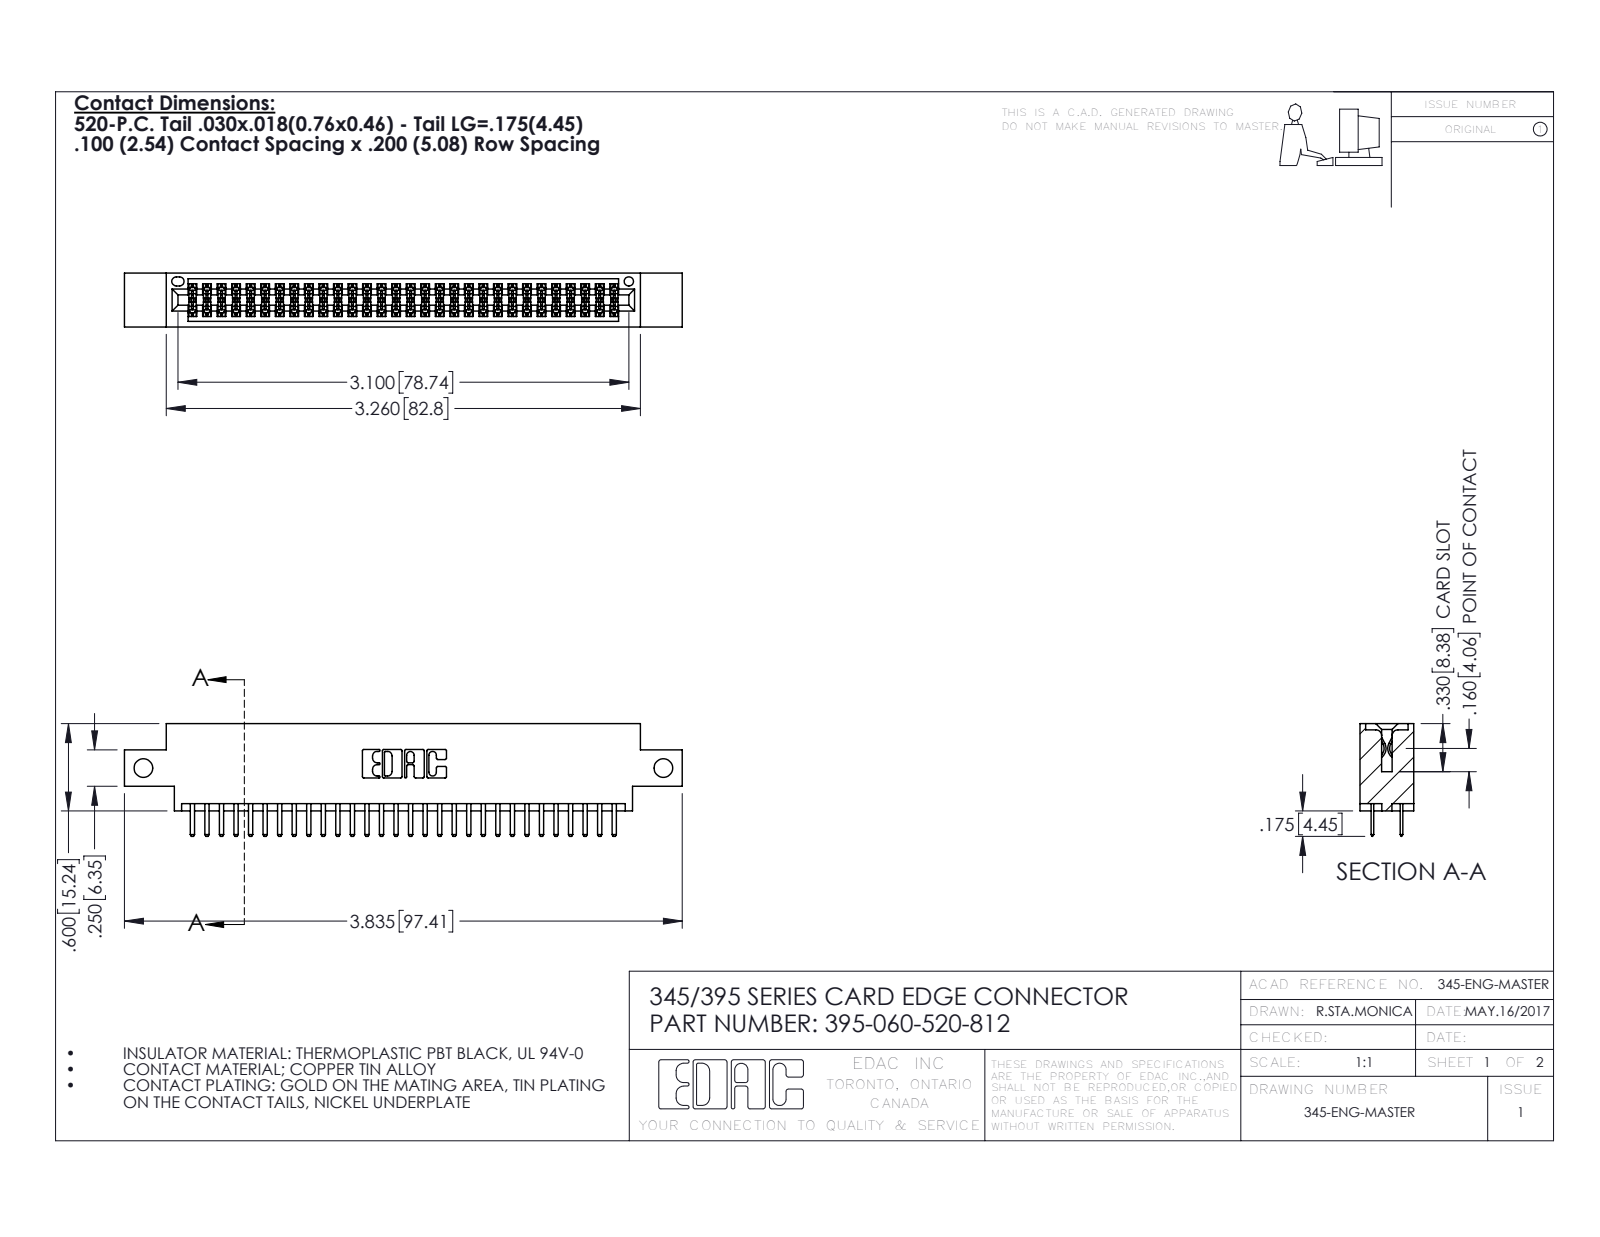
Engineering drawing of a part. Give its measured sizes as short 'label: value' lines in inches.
name: 395-060-520-812; 345-292-001_345-293-120; 345 Part_0.170 Offset - Side Mount
written by: SolidWorks 2016 (CONFIG_CONTROL_DESIGN)
unit: in
bodies: 61 solids, 3370 faces (2184 planar, 1186 cylindrical, 0 other)
size: 3.835 × 0.775 × 0.37
volume: 0.557 in³; area: 20.47 in²
holes: 2× ⌀0.128, 1× ⌀0.064
rounds: 90× R0.006, 64× R0.01, 22× R0.01, 6× R0.007, 6× R0.031, 3× R0.026, 2× R0.014, 2× R0.019
face distances: 0.298, 0.072, 0.2, 0.37, 0.098, 0.272, 0.025, 0.225, 0.022, 0.175
hole spacings: 3.575
